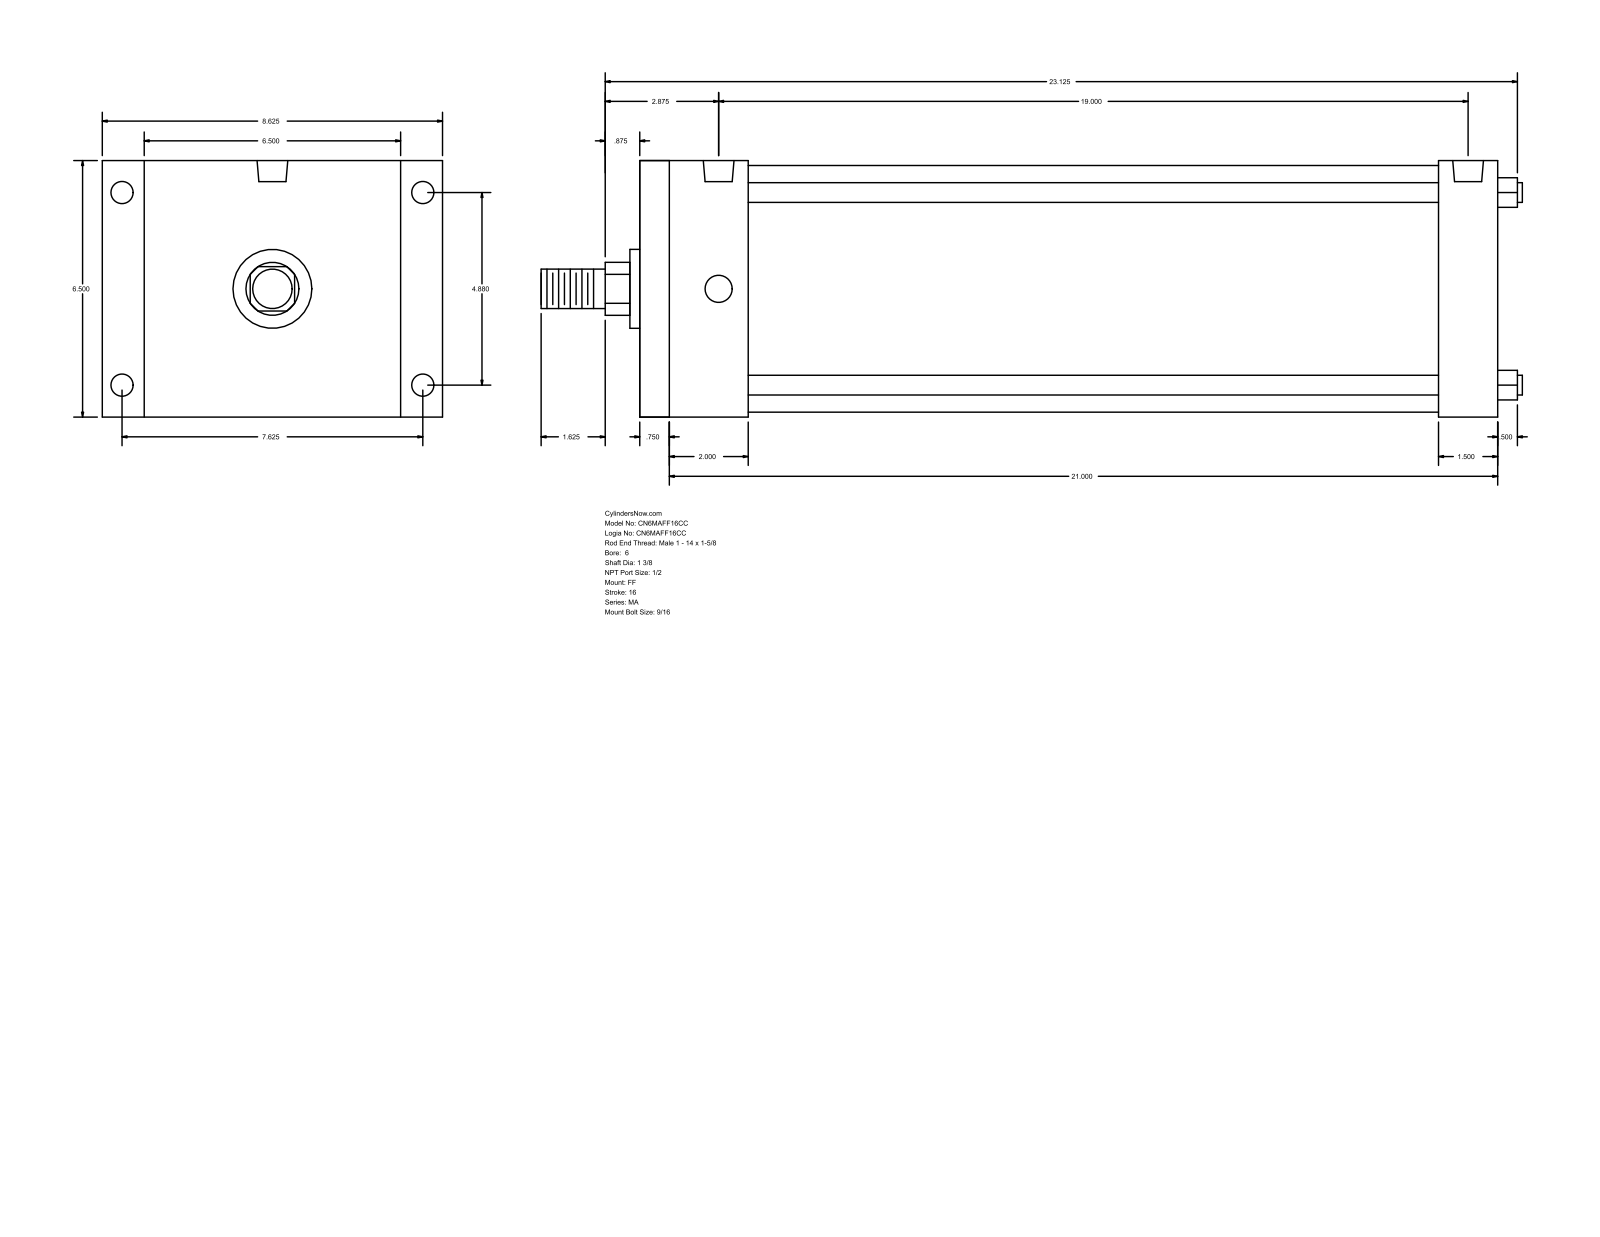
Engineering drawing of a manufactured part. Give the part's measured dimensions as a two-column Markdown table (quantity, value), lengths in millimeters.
| quantity | value |
| --- | --- |
| part name | MA_FF__0600_1.375 |
| STEP written by | GSSL Pune (CONFIG_CONTROL_DESIGN) |
| units | millimeters |
| bodies | 0 solids, 92 faces (64 planar, 28 cylindrical, 0 other) |
| overall size | 631.83 × 219.07 × 165.1 |
| round holes (diameter × count) | 14.29 × 4, 17.46 × 4, 19.77 × 2 |
| round bosses / shafts (diameter × count) | 12.7 × 4, 158.75 × 1, 50.8 × 1, 34.92 × 1, 25.4 × 1 |
| partial cylindrical surfaces (radius × count) | 17.06 × 1 |
| main face-to-face distances | 165.1, 552.44, 15.87, 536.57, 50.8, 498.48, 66.67, 485.77, 514.35, 447.68 |
| hole center spacings | 123.96, 193.68, 229.95, 485.77, 3.18, 482.59 |
